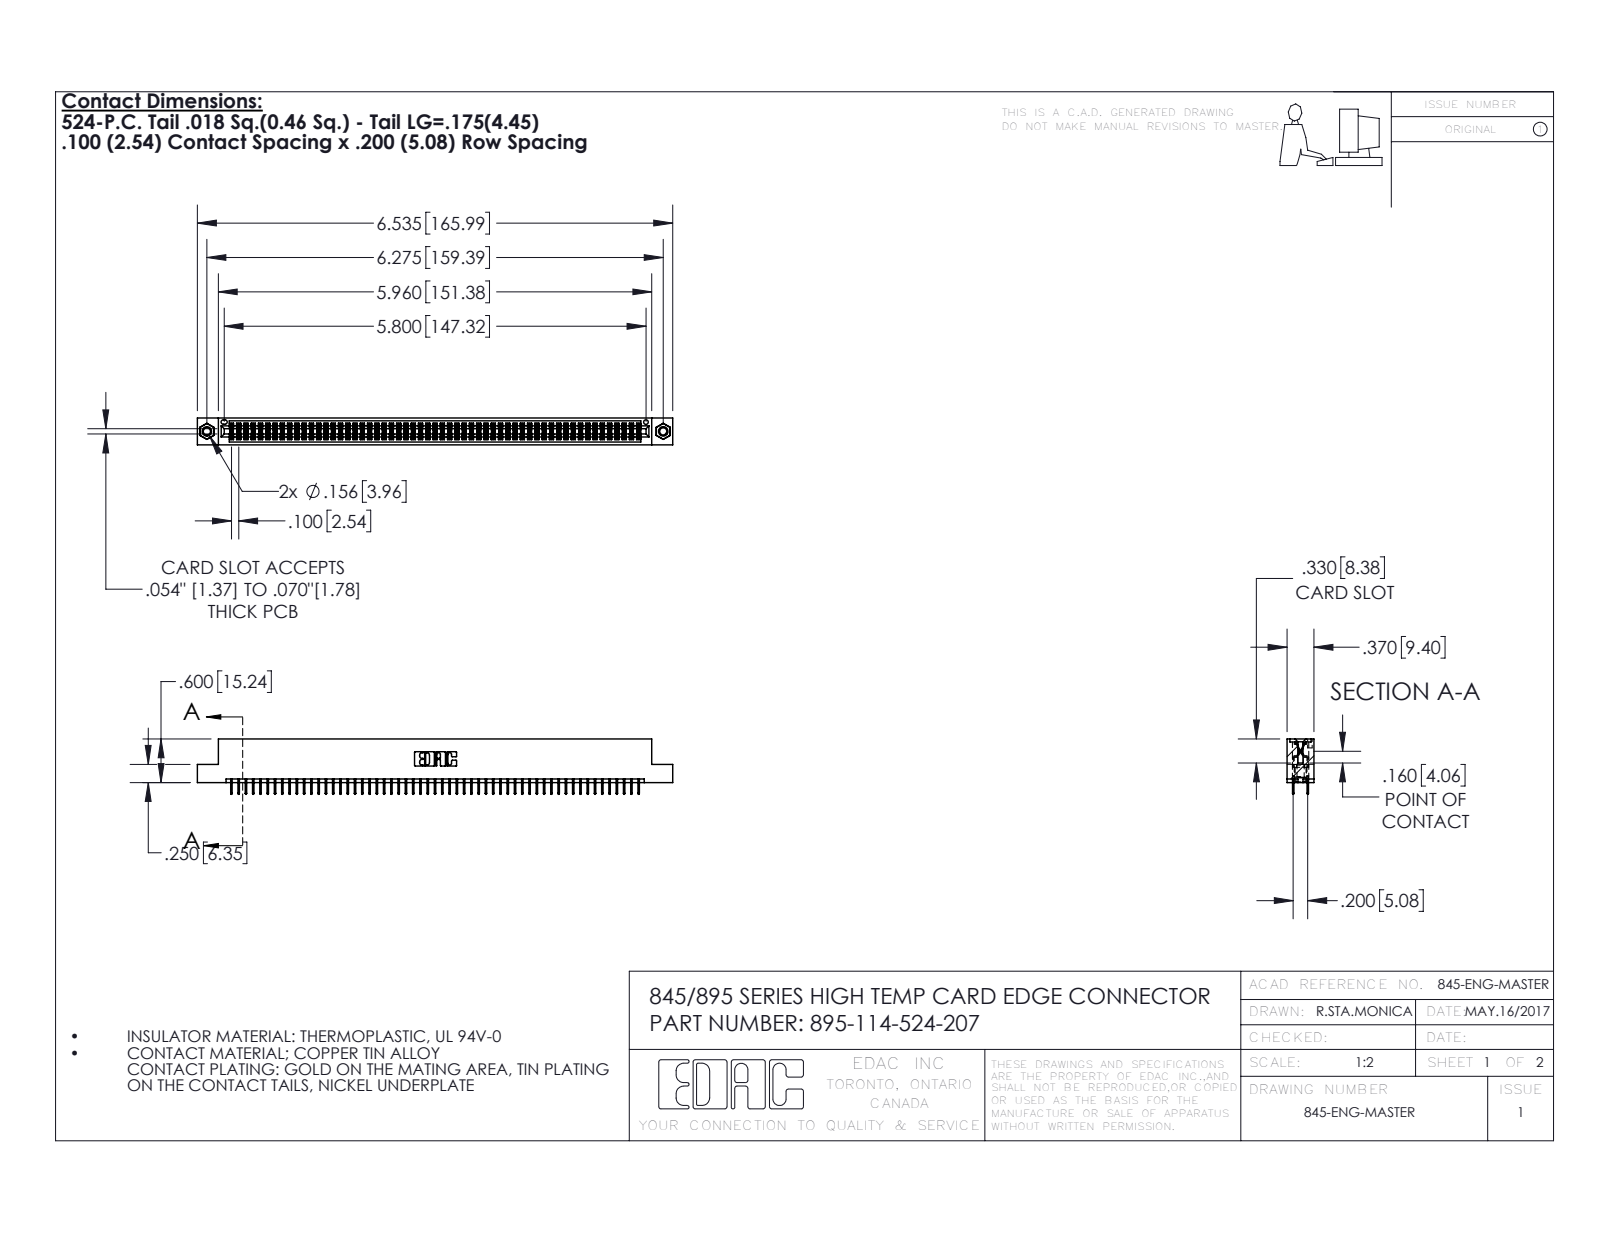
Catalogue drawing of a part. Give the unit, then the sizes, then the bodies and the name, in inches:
Units: inches
Overall size (bounding box): 6.535 × 0.762 × 0.37
Round holes (diameter × count): ⌀0.098 ×2, ⌀0.125 ×2, ⌀0.156 ×2, ⌀0.064 ×1
Round bosses / shafts (diameter × count): ⌀0.155 ×2
Partial cylindrical surfaces — rounded edges, fillets, slot ends (radius × count): R0.006 ×172, R0.01 ×22, R0.007 ×6, R0.031 ×6, R0.026 ×3, R0.014 ×2, R0.019 ×2, R0.022 ×2
Main face-to-face distances: 0.072, 0.298, 0.2, 0.37, 0.098, 0.272, 0.025, 0.225, 0.072, 0.175
Hole centre spacings: 0.27, 6.039, 6.275
Volume: 0.981 in³ · Surface area: 36.62 in²
Bodies: 117 solids, 6342 faces (4558 planar, 1768 cylindrical, 16 other)
Part name (STEP PRODUCT): 345-250-001_345-250-005-103; 345-292-001_345-293-124; 345 Part_Flush Mounting Lugs - 0.156 Dia-TI; 395-114-524-207
STEP written by: SolidWorks 2016 (CONFIG_CONTROL_DESIGN)
